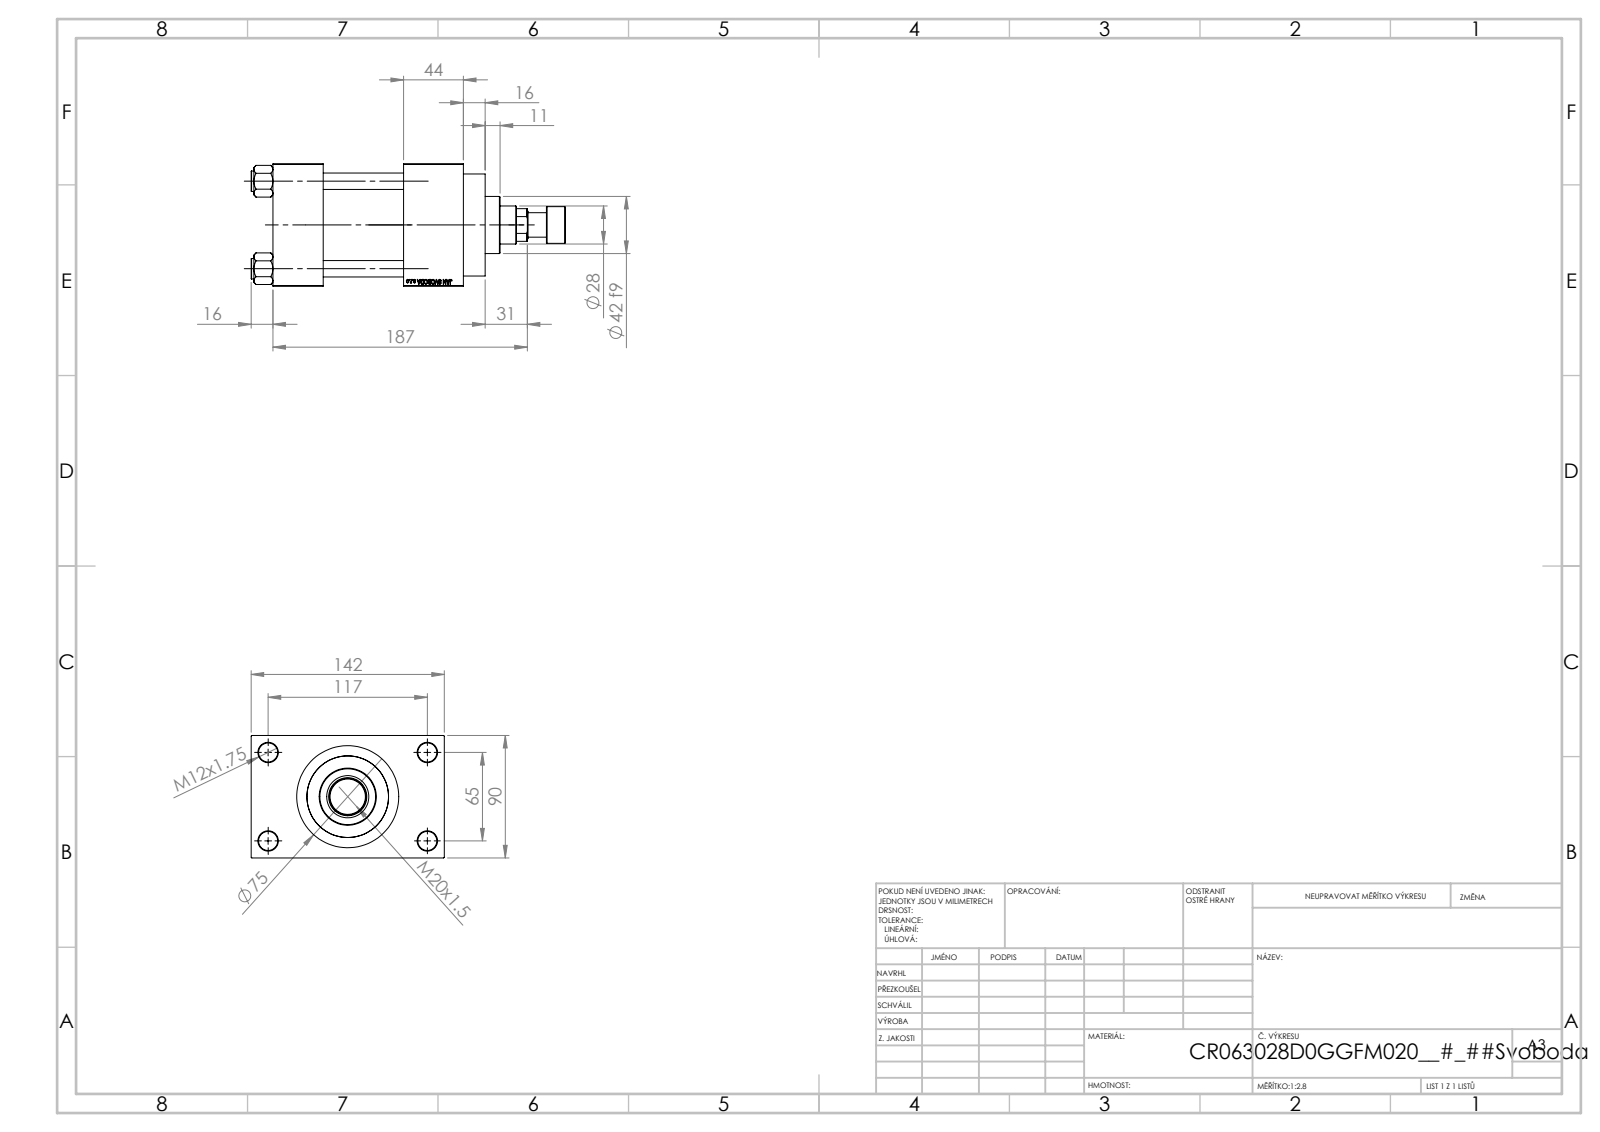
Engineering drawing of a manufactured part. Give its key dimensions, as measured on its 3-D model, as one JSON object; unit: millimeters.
{"part_name": "V215CR_D_TYCINKA; V215CR_VCP_D; NUT_M5_D; V215CR_D_Body (+2 more)", "step_written_by": "SolidWorks 2019 (CONFIG_CONTROL_DESIGN)", "units": "millimeters", "bodies": {"solids": 12, "faces": 1118, "planar": 501, "cylindrical": 93, "other": 524}, "overall_size": [231, 142, 90], "volume_mm3": 1117000, "surface_area_mm2": 201864, "round_holes": [[12, 4], [14, 4], [7, 2], [20.96, 2], [30, 2], [18.5, 1], [28, 1], [31, 1], [50, 1], [60, 1], [63, 1]], "round_bosses_or_shafts": [[15, 4], [75, 1], [69, 1], [42, 1], [27, 1], [18, 1]], "face_to_face_distances": [90, 59, 37, 96, 140, 103, 44, 26, 116, 142], "hole_center_spacings": [26.35, 45.47, 64.3, 66.92, 69.81, 90.65, 111.34, 65]}
